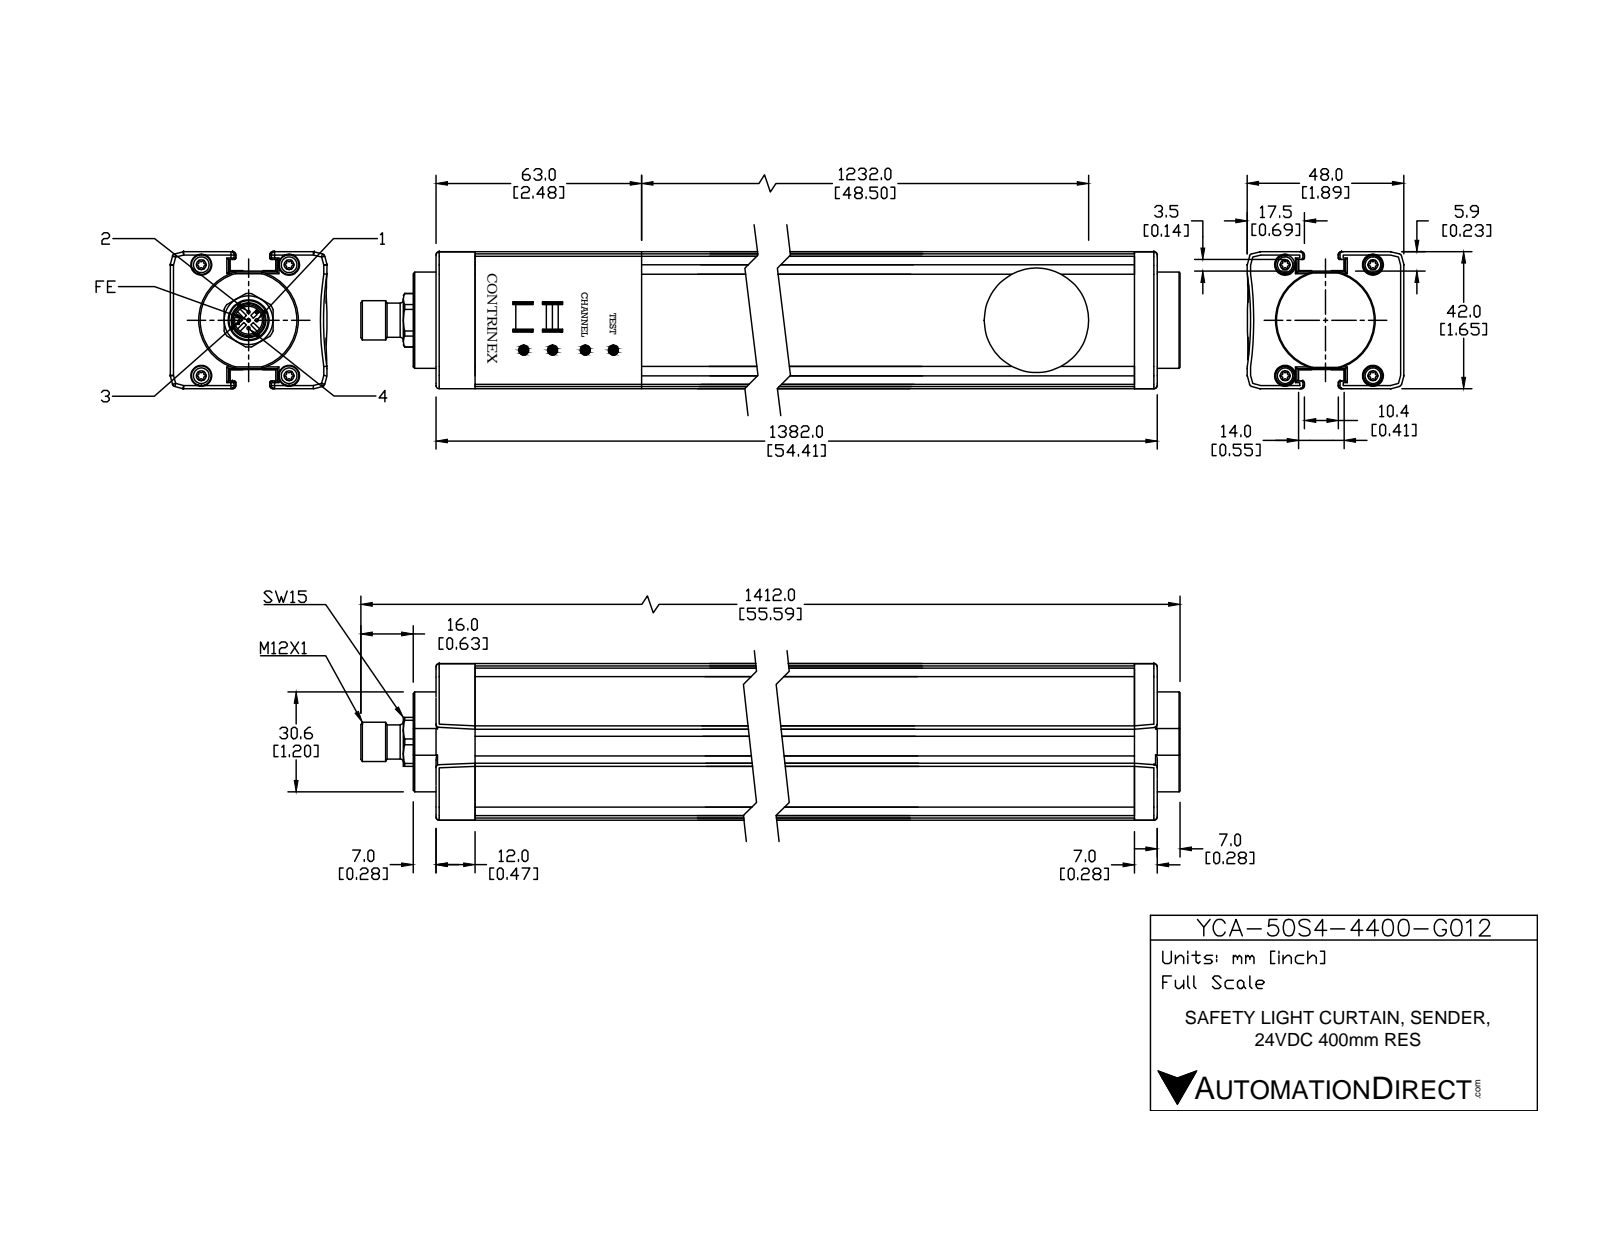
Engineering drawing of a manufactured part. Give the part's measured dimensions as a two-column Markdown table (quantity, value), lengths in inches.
| quantity | value |
| --- | --- |
| part name | YCA-50S4-4400-G012 |
| STEP written by | SolidWorks 2016 (AUTOMOTIVE_DESIGN) |
| units | inches |
| bodies | 18 solids, 454 faces (221 planar, 172 cylindrical, 61 other) |
| overall size | 55.591 × 1.89 × 1.654 |
| volume | 151.8 in³ |
| surface area | 488.3 in² |
| round holes (diameter × count) | 0.236 × 4, 0.039 × 1, 0.335 × 1, 1.26 × 1 |
| round bosses / shafts (diameter × count) | 0.217 × 4, 0.039 × 4, 1.205 × 1, 0.472 × 1, 0.413 × 1 |
| partial cylindrical surfaces (radius × count) | 0.039 × 52, 0.02 × 4, 0.323 × 1, 3.937 × 1 |
| main face-to-face distances | 1.654, 0.228, 1.425, 1.157, 0.039, 0.268, 1.386, 1.197, 0.551, 0.677 |
| hole center spacings | 0.828, 0.88, 1.059, 1.339, 1.707 |
